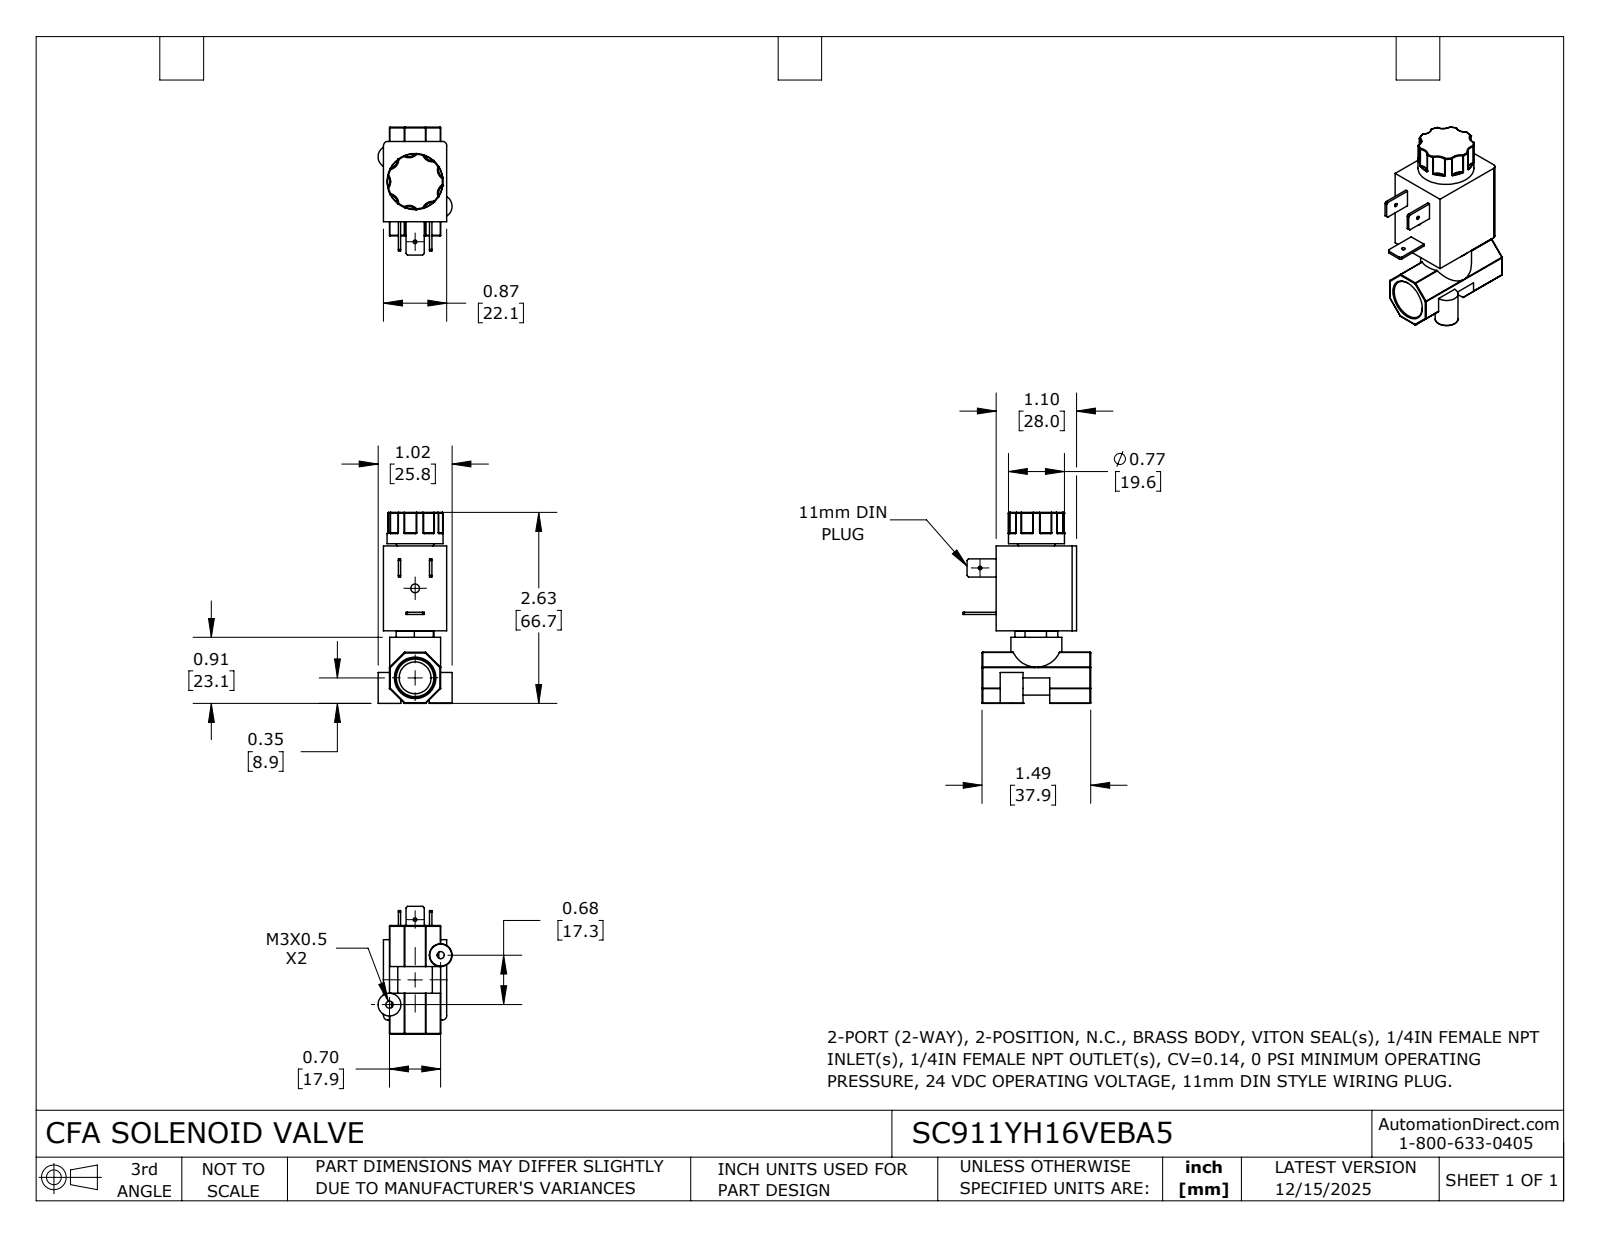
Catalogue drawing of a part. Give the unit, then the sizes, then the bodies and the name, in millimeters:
Units: millimetres
Overall size (bounding box): 66.7 × 44.6 × 25.8
Round holes (diameter × count): ⌀1.3 ×2, ⌀2.5 ×2, ⌀3 ×1, ⌀11.1 ×1
Round bosses / shafts (diameter × count): ⌀8 ×2, ⌀19.6 ×1, ⌀17.8 ×1
Partial cylindrical surfaces — rounded edges, fillets, slot ends (radius × count): R0.3 ×42, R3.4 ×7, R1.5 ×2, R3.4 ×2, R6 ×1, R8.3 ×1
Main face-to-face distances: 22.1, 17.9, 28, 29.6, 2.1, 20, 11.7, 25.3, 55, 66.7
Hole centre spacings: 15.3, 24.9, 31, 31.2
Volume: 29 460 mm³ · Surface area: 10 410 mm²
Bodies: 1 solid, 314 faces (74 planar, 91 cylindrical, 149 other)
Part name (STEP PRODUCT): SC911YH16VEBA5
STEP written by: SolidWorks 2024 (CONFIG_CONTROL_DESIGN)
